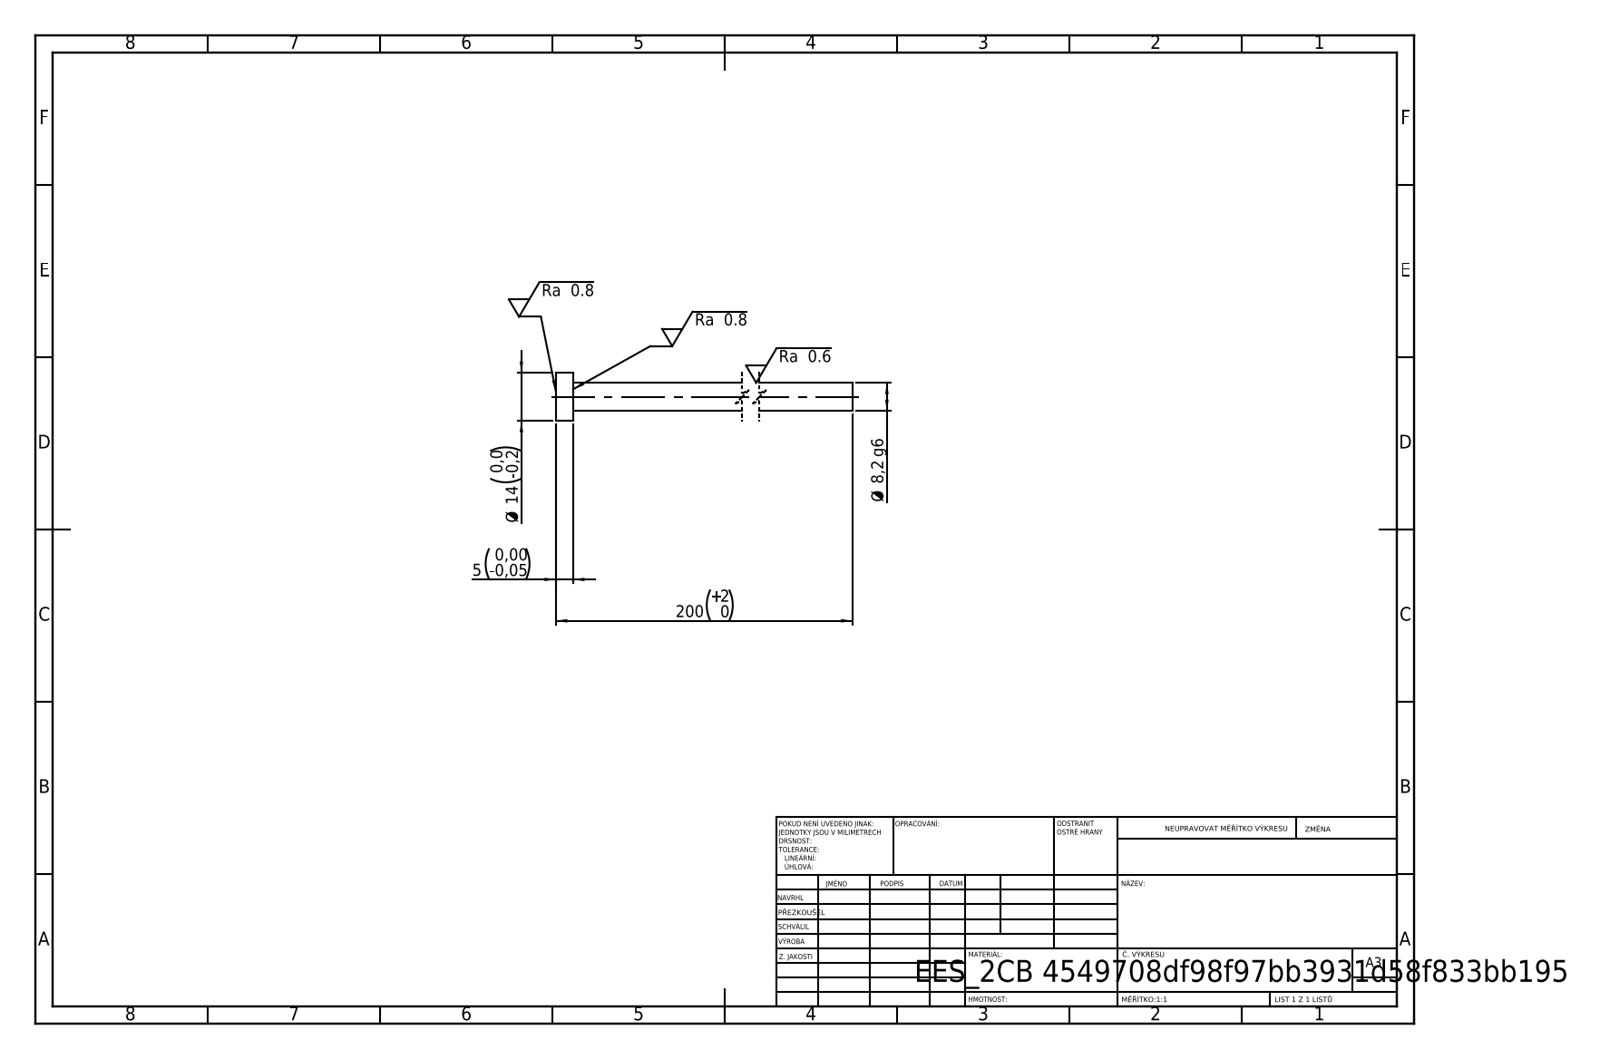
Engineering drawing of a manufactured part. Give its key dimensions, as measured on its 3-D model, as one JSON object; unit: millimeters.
{"step_written_by": "SolidWorks 2019 (CONFIG_CONTROL_DESIGN)", "units": "millimeters", "bodies": {"solids": 1, "faces": 7, "planar": 3, "cylindrical": 4, "other": 0}, "overall_size": [200, 14, 14], "volume_mm3": 11068, "surface_area_mm2": 5551, "round_bosses_or_shafts": [[14, 1], [8.2, 1]], "face_to_face_distances": [5, 200, 195]}
